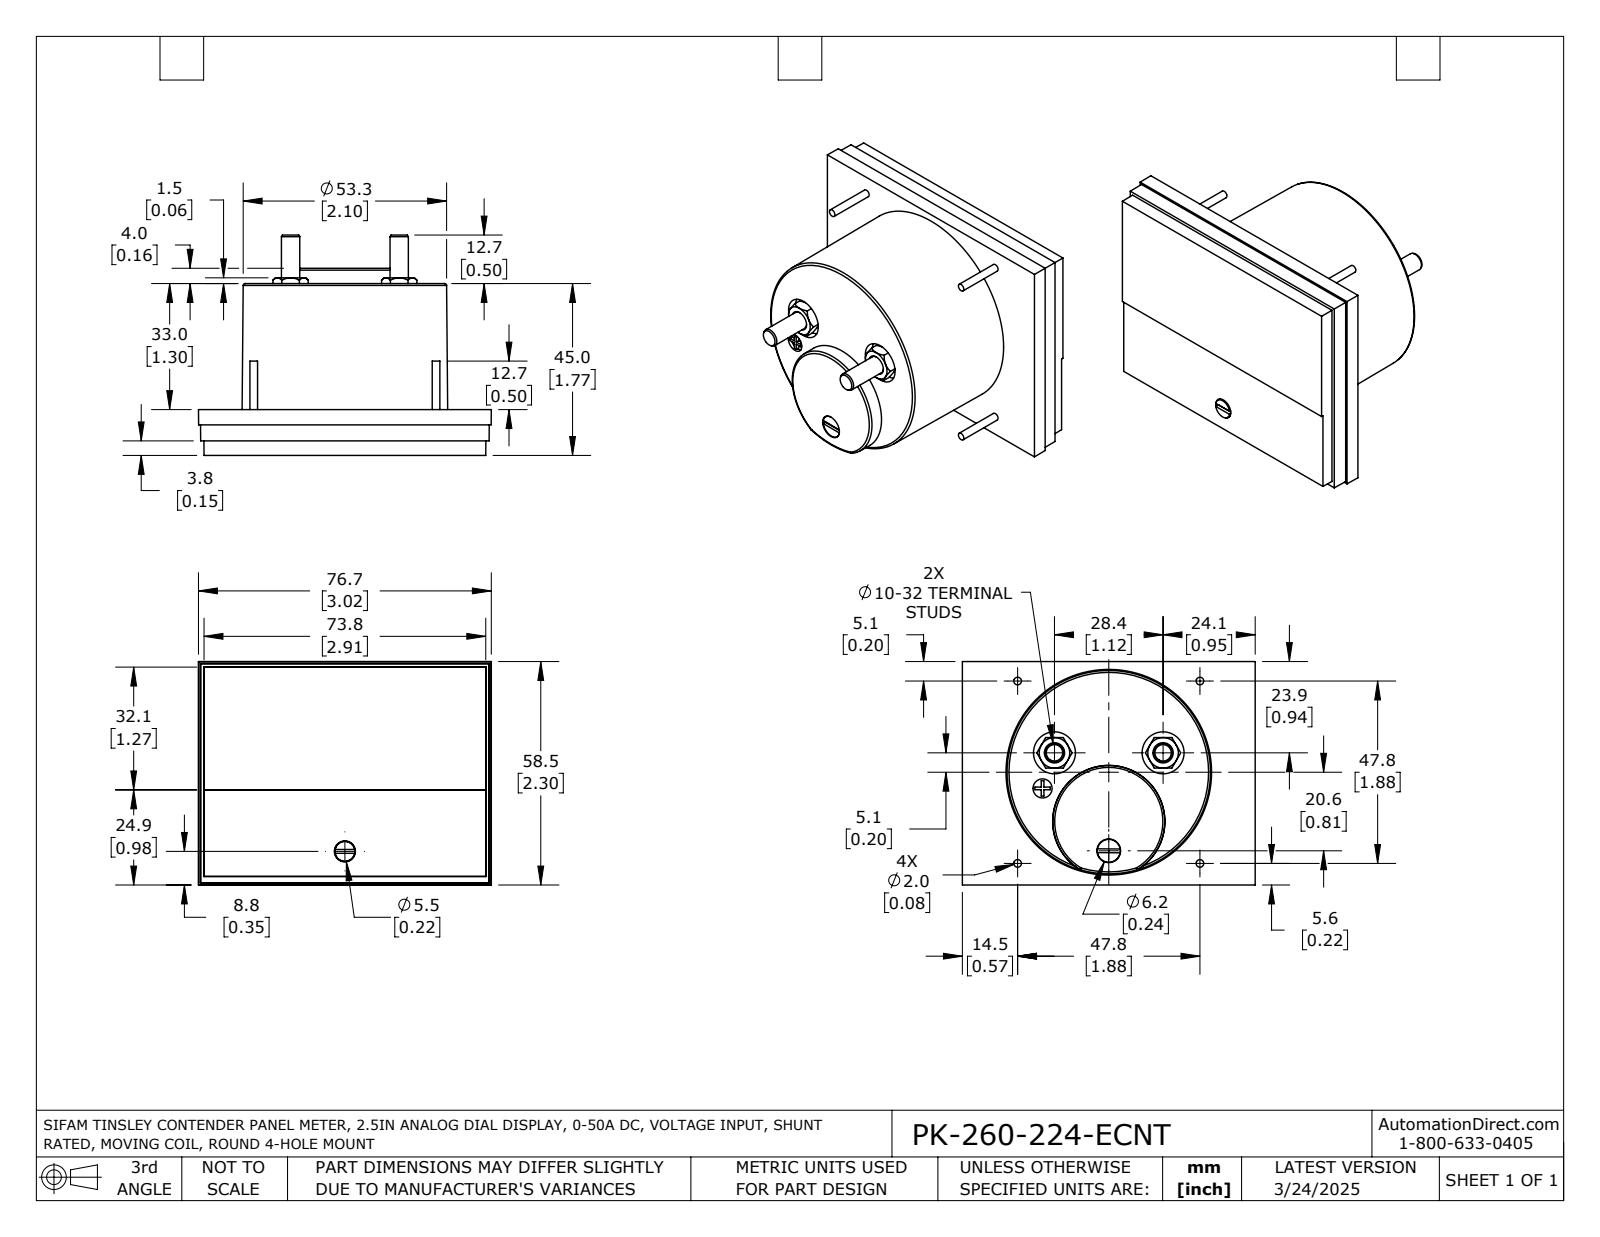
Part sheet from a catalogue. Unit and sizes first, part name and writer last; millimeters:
Units: millimetres
Overall size (bounding box): 76.7 × 58.5 × 57.7
Round holes (diameter × count): ⌀5 ×3, ⌀11 ×2, ⌀5.3 ×1, ⌀5.5 ×1, ⌀6.2 ×1
Round bosses / shafts (diameter × count): ⌀2 ×4, ⌀4.8 ×2, ⌀6 ×1, ⌀5.2 ×1
Partial cylindrical surfaces — rounded edges, fillets, slot ends (radius × count): R0.8 ×1
Main face-to-face distances: 0.5, 12, 3.3, 8.2, 3.8, 11.5, 1.4, 2, 10.1, 1.9
Hole centre spacings: 29.3, 29.5, 9.8, 23.8, 23.9, 28.4, 32.9
Volume: 125 500 mm³ · Surface area: 23 580 mm²
Bodies: 1 solid, 192 faces (95 planar, 37 cylindrical, 60 other)
Part name (STEP PRODUCT): PK-260-224-ECNT
STEP written by: SolidWorks 2021 (AUTOMOTIVE_DESIGN)
